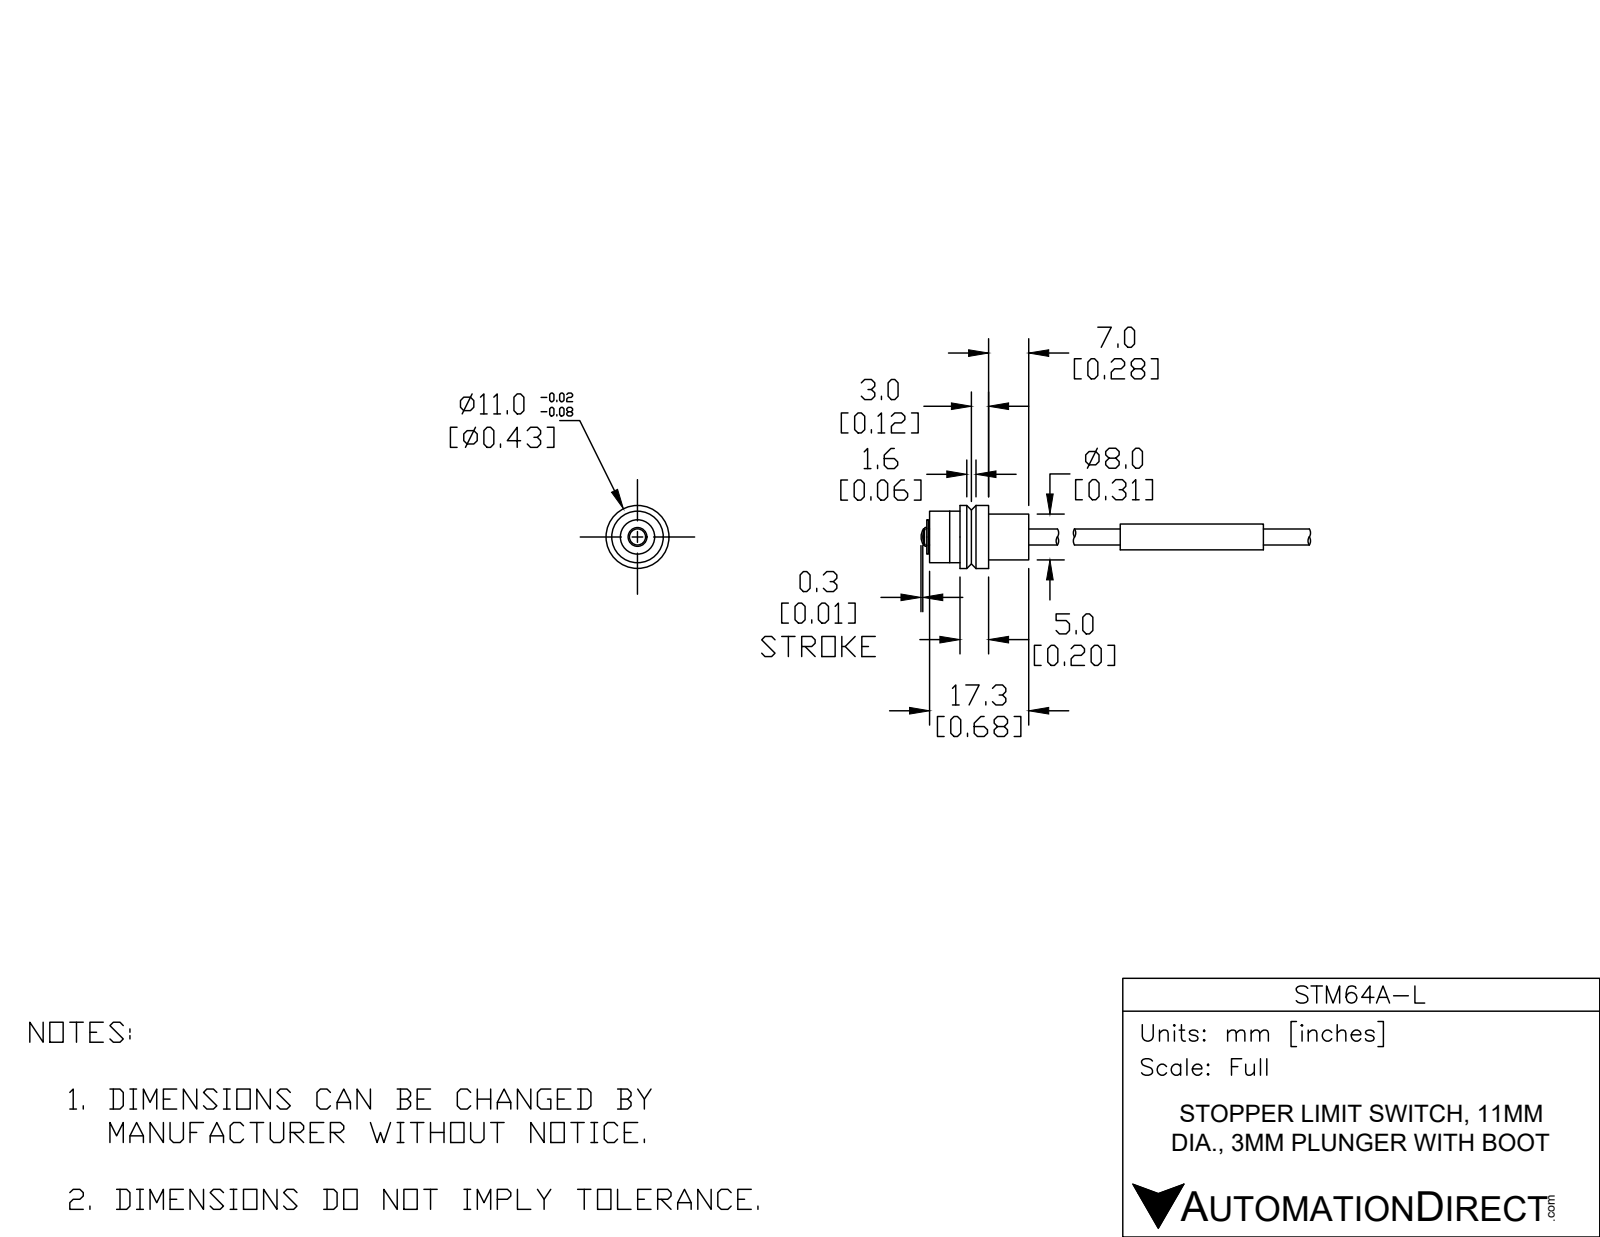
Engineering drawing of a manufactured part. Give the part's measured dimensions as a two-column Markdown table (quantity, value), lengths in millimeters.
| quantity | value |
| --- | --- |
| part name | STM64A-L |
| STEP written by | SolidWorks 2017 (CONFIG_CONTROL_DESIGN) |
| units | millimeters |
| bodies | 2 solids, 45 faces (13 planar, 24 cylindrical, 8 other) |
| overall size | 69.8 × 11 × 11 |
| volume | 1 694 mm³ |
| surface area | 1 360 mm² |
| round bosses / shafts (diameter × count) | 11 × 1, 9 × 1, 8.8 × 1, 8 × 1, 6 × 1, 4.5 × 1, 2.8 × 1 |
| main face-to-face distances | 10.3, 17.3, 7, 5.3, 5, 12, 5.5, 10.5, 17.5, 0.5 |
